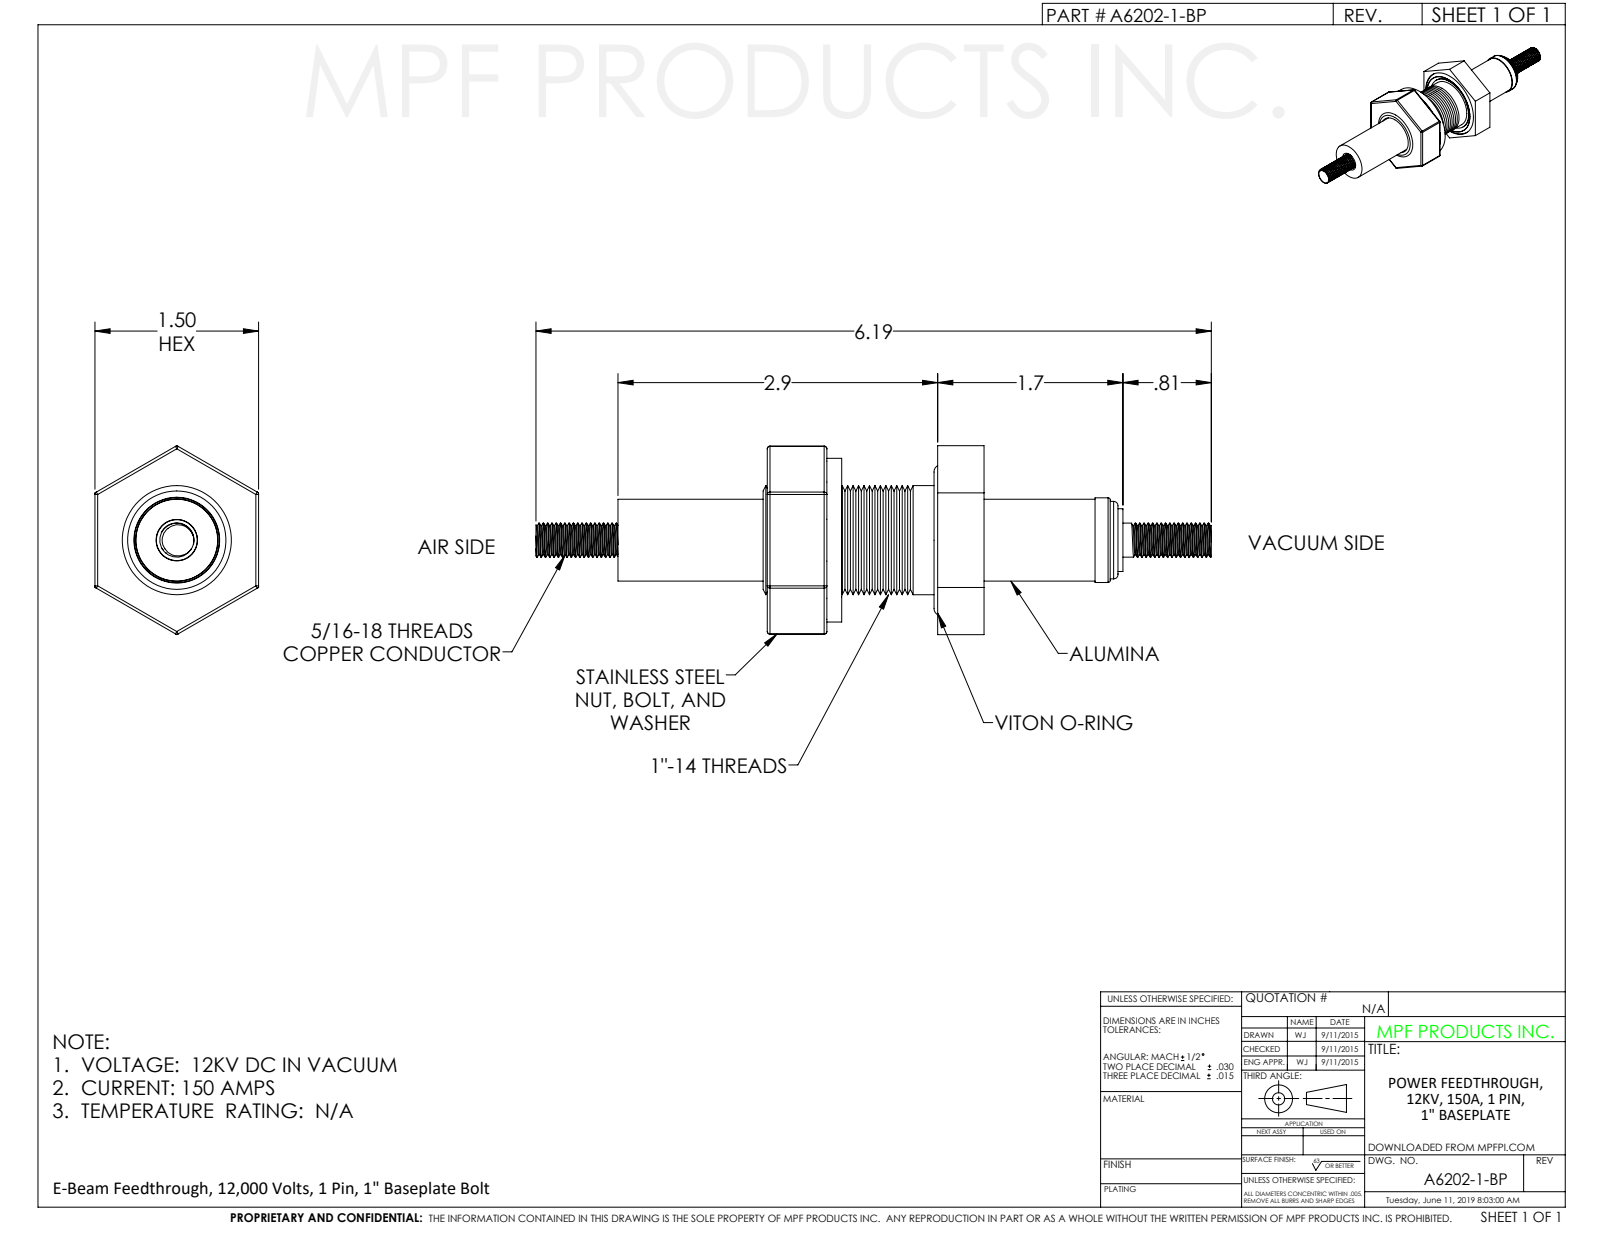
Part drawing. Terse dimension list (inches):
name: A6202-1
written by: SolidWorks 2019 (CONFIG_CONTROL_DESIGN)
unit: in
bodies: 1 solid, 343 faces (44 planar, 121 cylindrical, 178 other)
size: 6.19 × 1.732 × 1.5
volume: 3.98 in³; area: 32.96 in²
holes: 1× ⌀1.035, 1× ⌀1.305, 1× ⌀1.39
bosses: 1× ⌀1.5, 1× ⌀1.368, 1× ⌀1.11, 1× ⌀1, 1× ⌀0.776, 1× ⌀0.75, 1× ⌀0.71, 1× ⌀0.575
rounds: 18× R0.025
face distances: 1.5, 1.987, 1.305, 0.682, 0.425, 0.88, 1.562, 0.32, 0.105, 0.985
